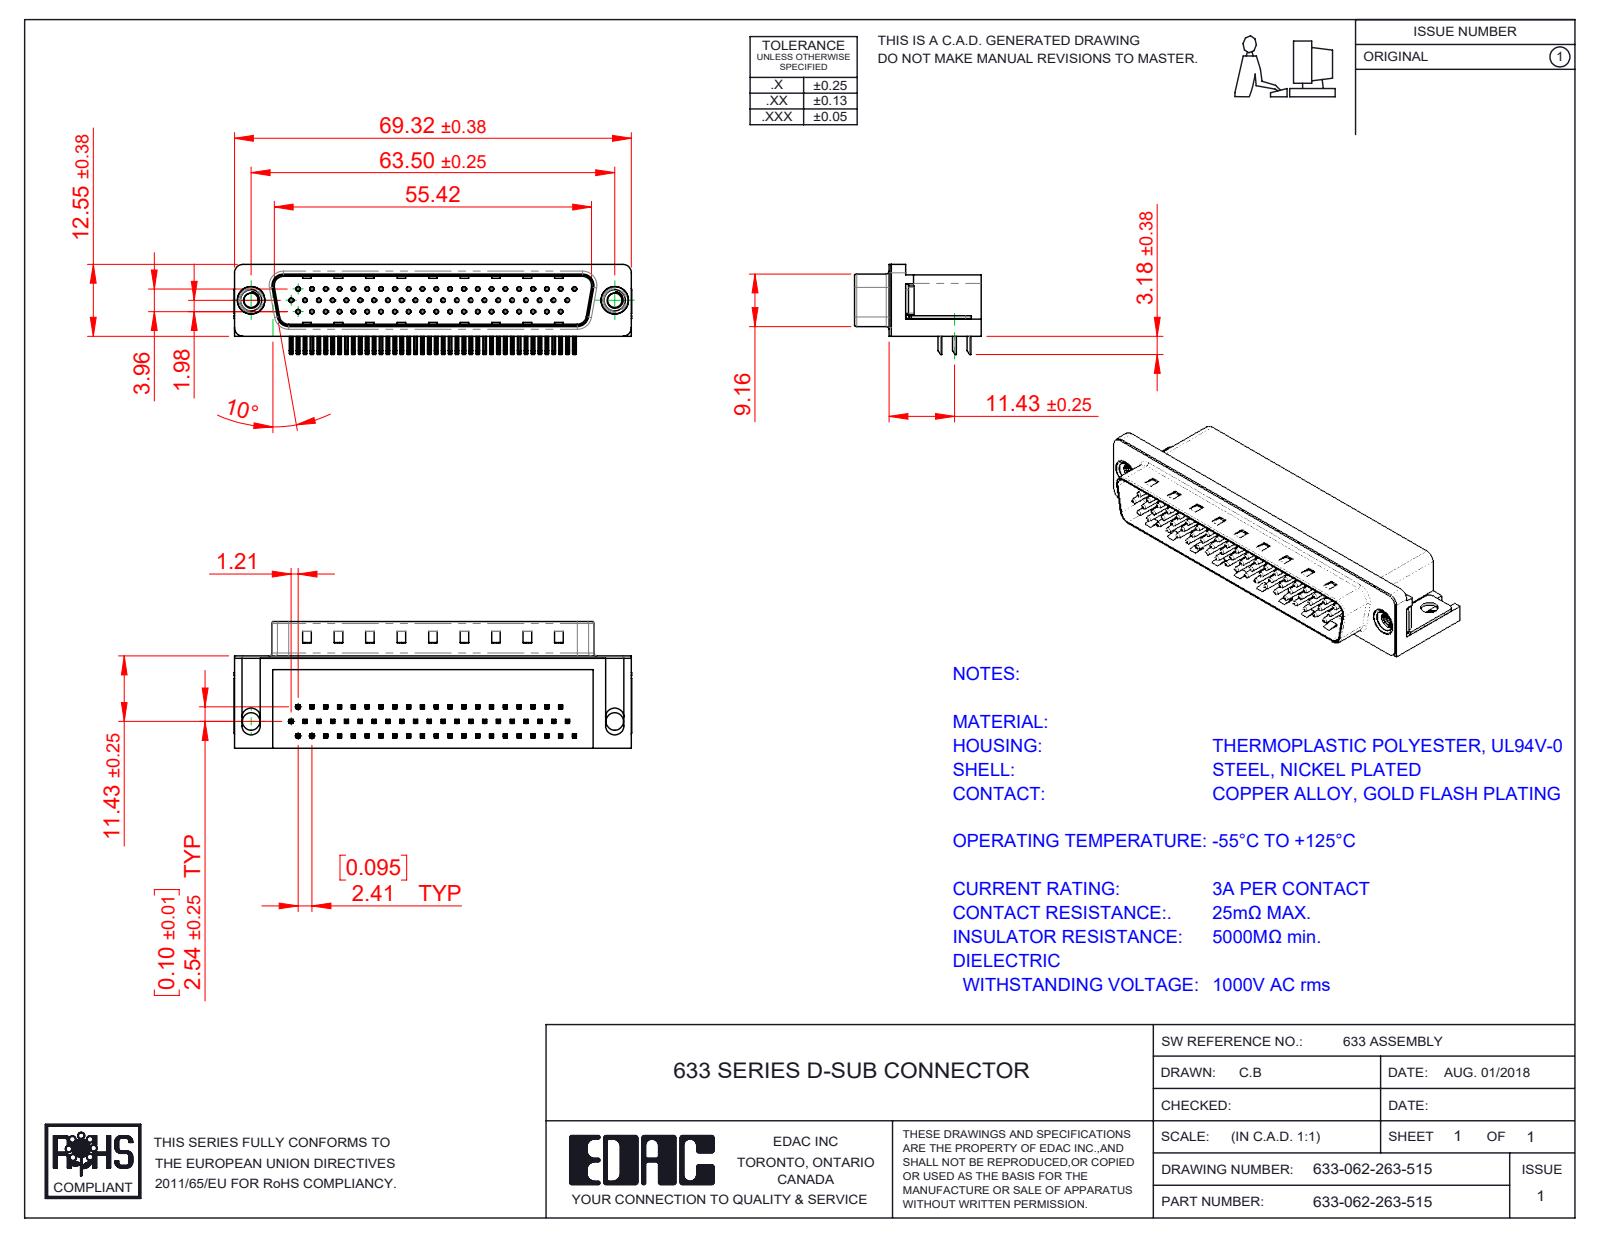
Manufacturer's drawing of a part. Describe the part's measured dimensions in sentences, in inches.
The part is named "633 Contact Bottom; 633 Contact Middle; 633 Contact Top; 633 Thru Hole Board Mount (+4 more)". Its 3-D file was written by "SolidWorks 2016 (CONFIG_CONTROL_DESIGN)". It is 68 solids with 5074 faces: 3211 planar, 1446 cylindrical and 417 other. Overall it measures 2.732 by 0.87 by 0.619 inches. Its volume is 0.674 cubic inches and its surface area 20.76 square inches. Round holes: 62 of diameter 0.014, 62 of diameter 0.031, 2 of diameter 0.098, 2 of diameter 0.12, 2 of diameter 0.157, 2 of diameter 0.189, 2 of diameter 0.197. Round bosses or shafts: 62 of diameter 0.03, 2 of diameter 0.193, 2 of diameter 0.187, 2 of diameter 0.154. Partial cylindrical surfaces (rounded edges, fillets, slot ends): 256 of radius 0.01, 124 of radius 0.005, 16 of radius 0.039, 9 of radius 0.02, 8 of radius 0.063, 7 of radius 0.059, 4 of radius 0.035, 4 of radius 0.079. The main face-to-face distances are 0.016, 0.407, 0.618, 0.345, 0.114, 0.098, 0.1, 0.329, 0.083, 0.634. The hole center spacings are 0.095, 0.19, 0.285, 0.38, 0.57, 0.665, 0.19, 0.285.
